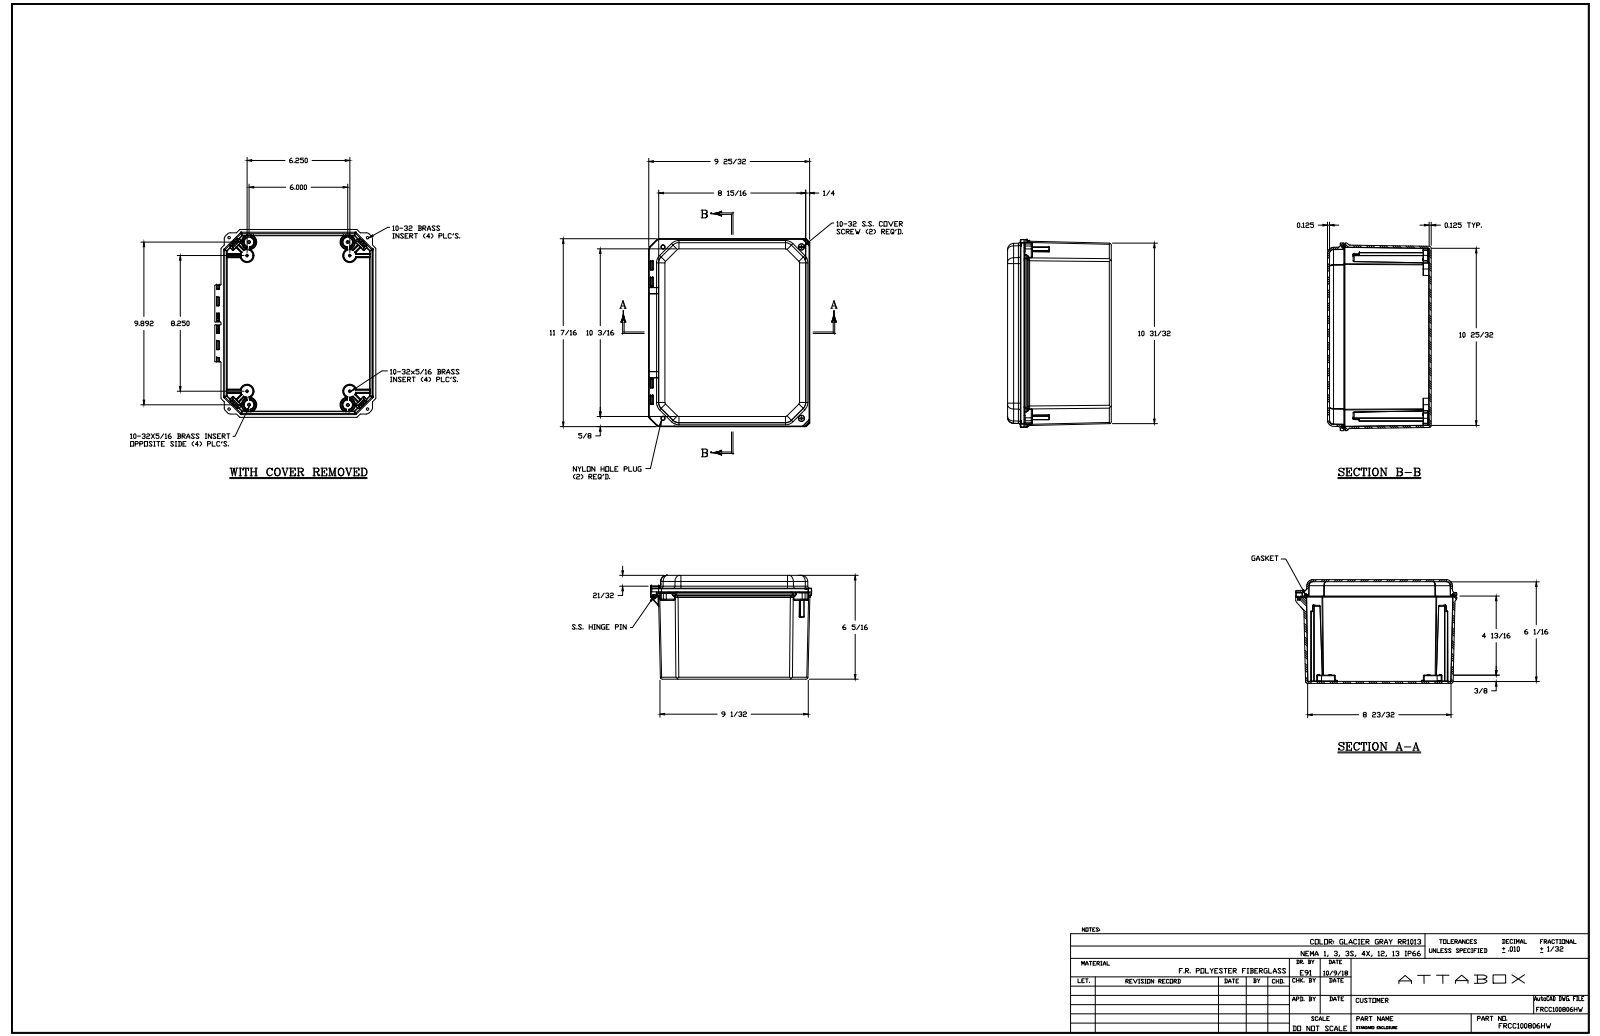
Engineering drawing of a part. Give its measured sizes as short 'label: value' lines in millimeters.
name: FRCC100806HW
written by: SolidWorks 2018 (AUTOMOTIVE_DESIGN)
unit: mm
bodies: 23 solids, 2000 faces (546 planar, 754 cylindrical, 700 other)
size: 290.2 × 248.9 × 160.3
volume: 1 023 000 mm³; area: 616 000 mm²
holes: 12× ⌀4, 8× ⌀3.9, 4× ⌀5.6, 4× ⌀6.4, 4× ⌀7.9, 2× ⌀3.8, 1× ⌀3.5
bosses: 12× ⌀6.2, 4× ⌀22.1, 2× ⌀11.4, 2× ⌀5.3, 2× ⌀5.1, 1× ⌀3.4, 1× ⌀3.4
rounds: 188× R0.3, 94× R0.1, 59× R0.5, 37× R0.8, 29× R3.2, 24× R0.8, 24× R2.3, 24× R6.4
face distances: 3.2, 157.1, 3.2, 3.2, 160.3, 154, 140.5, 16.7, 6.4, 25.4
hole spacings: 21.1, 209.6, 230.4, 238.7, 301.6, 262.9, 31.5, 39
